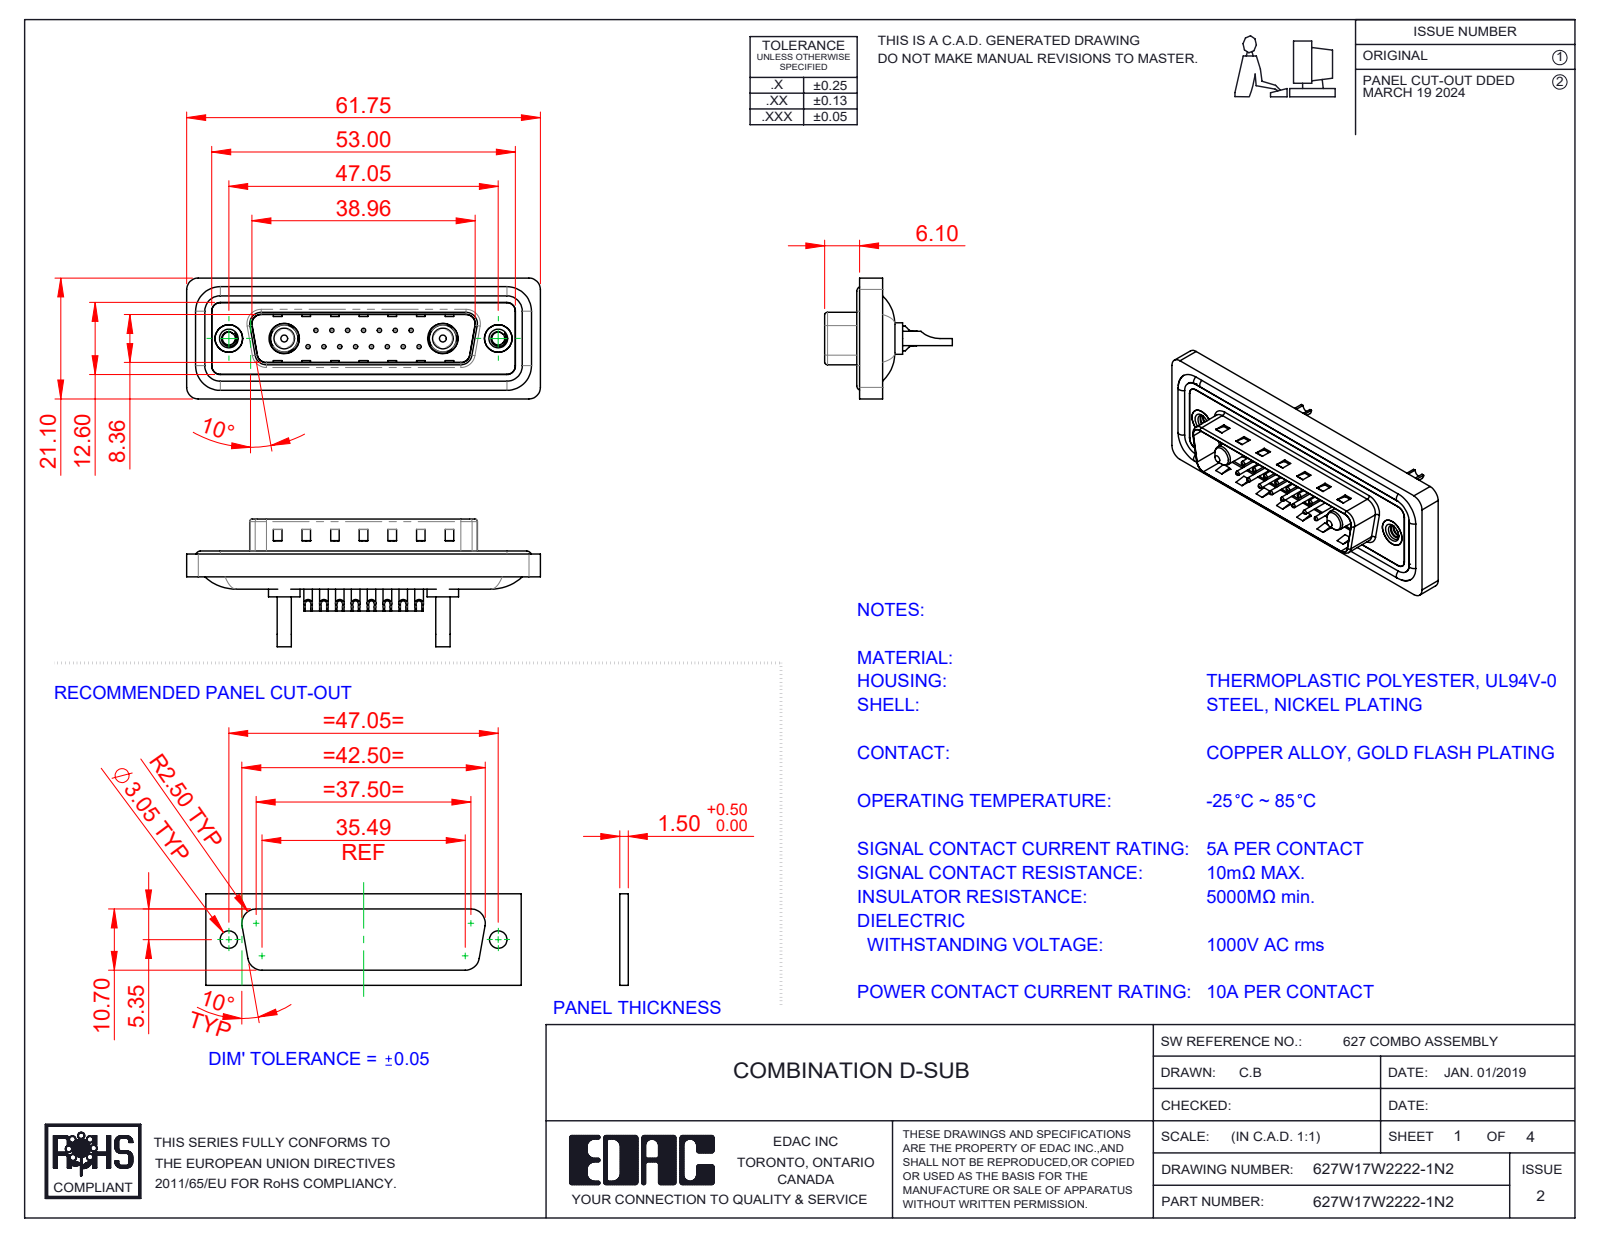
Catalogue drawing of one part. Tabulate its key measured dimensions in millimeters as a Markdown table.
| quantity | value |
| --- | --- |
| part name | 627W17W2222-1N2; 627Combo Housing_17W2; Power Pin_10A SC; 627Combo Contact Row 1_22 (+5 more) |
| STEP written by | SolidWorks 2023 (CONFIG_CONTROL_DESIGN) |
| units | millimeters |
| bodies | 26 solids, 1128 faces (368 planar, 472 cylindrical, 288 other) |
| overall size | 61.75 × 22.3 × 21.1 |
| volume | 7 284 mm³ |
| surface area | 12 129 mm² |
| round holes (diameter × count) | 0.75 × 15, 1 × 15, 1.6 × 15, 2 × 15, 1.7 × 2, 2.26 × 2, 4 × 2, 4.8 × 2, 4.85 × 2, 5 × 2, 5.3 × 2 |
| round bosses / shafts (diameter × count) | 1.5 × 15, 1.6 × 4, 5.5 × 2, 5.2 × 2, 4.9 × 2, 4.75 × 2, 3.75 × 2, 3.6 × 2 |
| partial cylindrical surfaces (radius × count) | 1.5 × 22, 2 × 18, 0.5 × 8, 1.6 × 8, 1 × 6, 0.25 × 4, 0.6 × 4, 0.65 × 4 |
| main face-to-face distances | 0.4, 1.5, 1.1, 1.6, 0.5, 3.1, 2.9, 0.82, 9.58, 4.1 |
| hole center spacings | 3.16, 2.77, 5.54, 8.31, 5.04, 7.49, 11.08, 5.03 |
